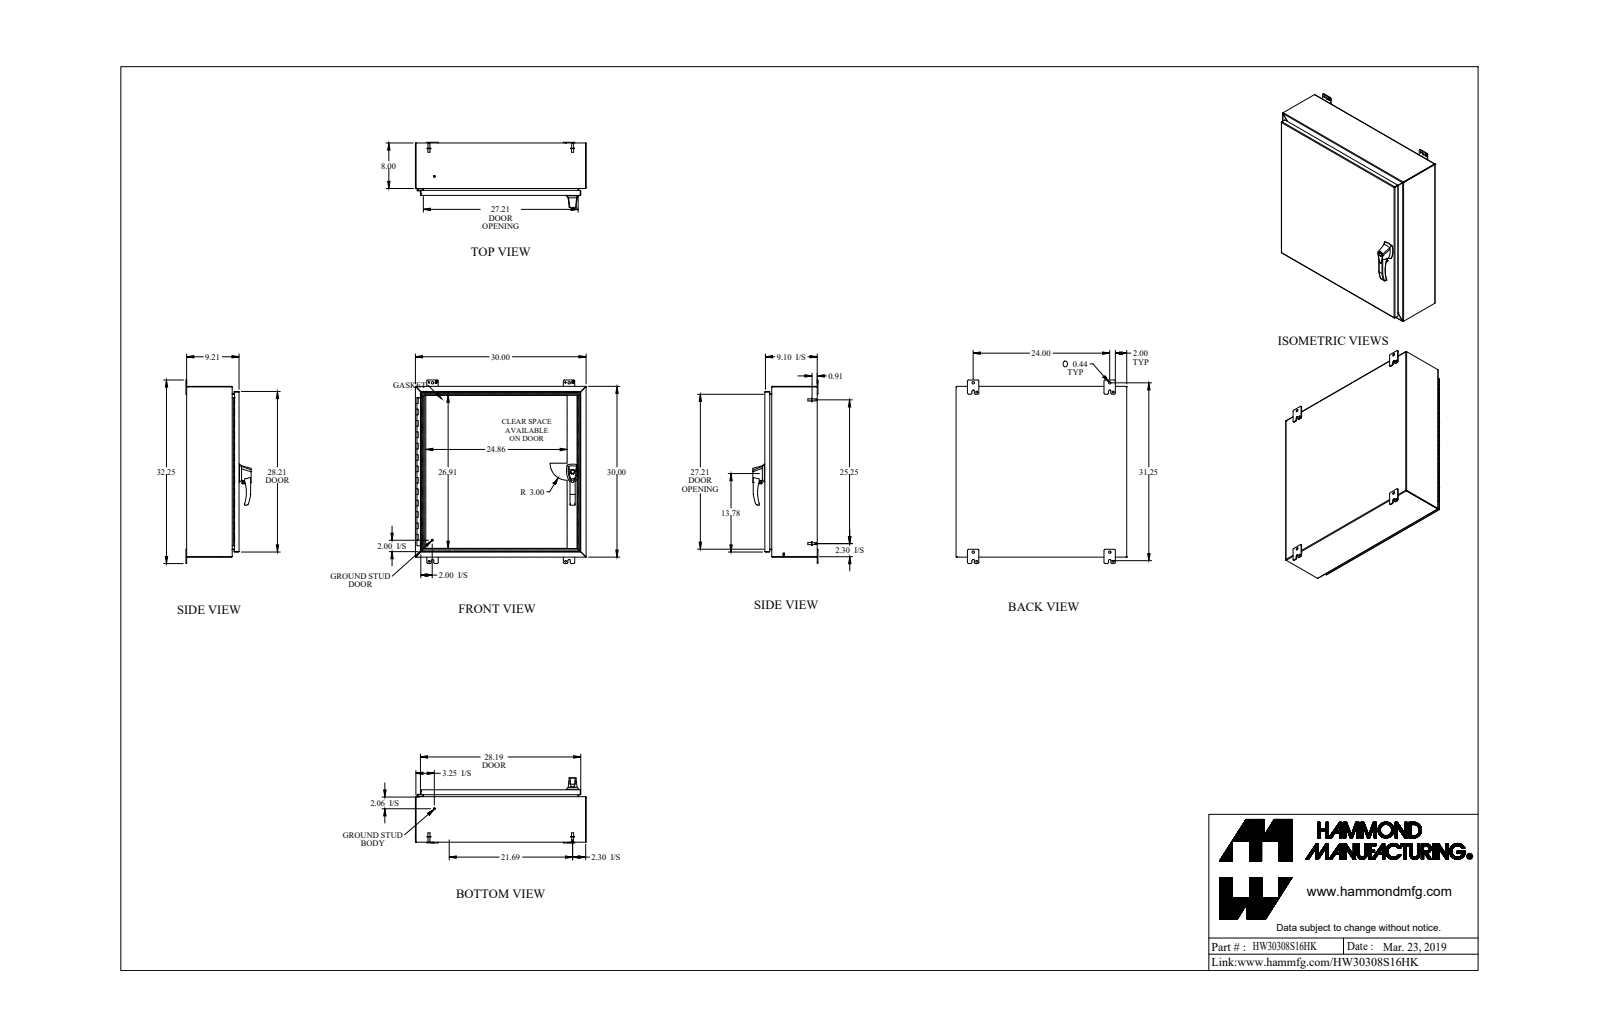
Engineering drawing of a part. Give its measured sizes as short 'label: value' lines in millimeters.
name: HW30308S16HK
written by: SolidWorks 2018 (AUTOMOTIVE_DESIGN)
unit: mm
bodies: 42 solids, 1456 faces (691 planar, 613 cylindrical, 152 other)
size: 819.2 × 762 × 290.8
volume: 4 185 000 mm³; area: 4 306 000 mm²
holes: 6× ⌀4.5, 5× ⌀8, 3× ⌀6.4, 3× ⌀6.7, 3× ⌀10.5, 2× ⌀5, 2× ⌀6.5, 2× ⌀10, 2× ⌀11.1, 1× ⌀2.8, 1× ⌀5.9, 1× ⌀8.4
bosses: 9× ⌀9.5, 7× ⌀6.4, 6× ⌀4, 4× ⌀16.5, 4× ⌀8.4, 4× ⌀8, 3× ⌀25.4, 3× ⌀13
rounds: 27× R6.4, 24× R4.8, 20× R0.9, 20× R2.7, 12× R1.5, 9× R3.2, 8× R1.1, 8× R5.5
face distances: 1.8, 760.2, 1.8, 232.1, 230.3, 232.1, 233.9, 758.3, 762, 201.4
hole spacings: 28.2, 282.4, 282.4, 564.8, 34, 248.4, 268.3, 268.4
